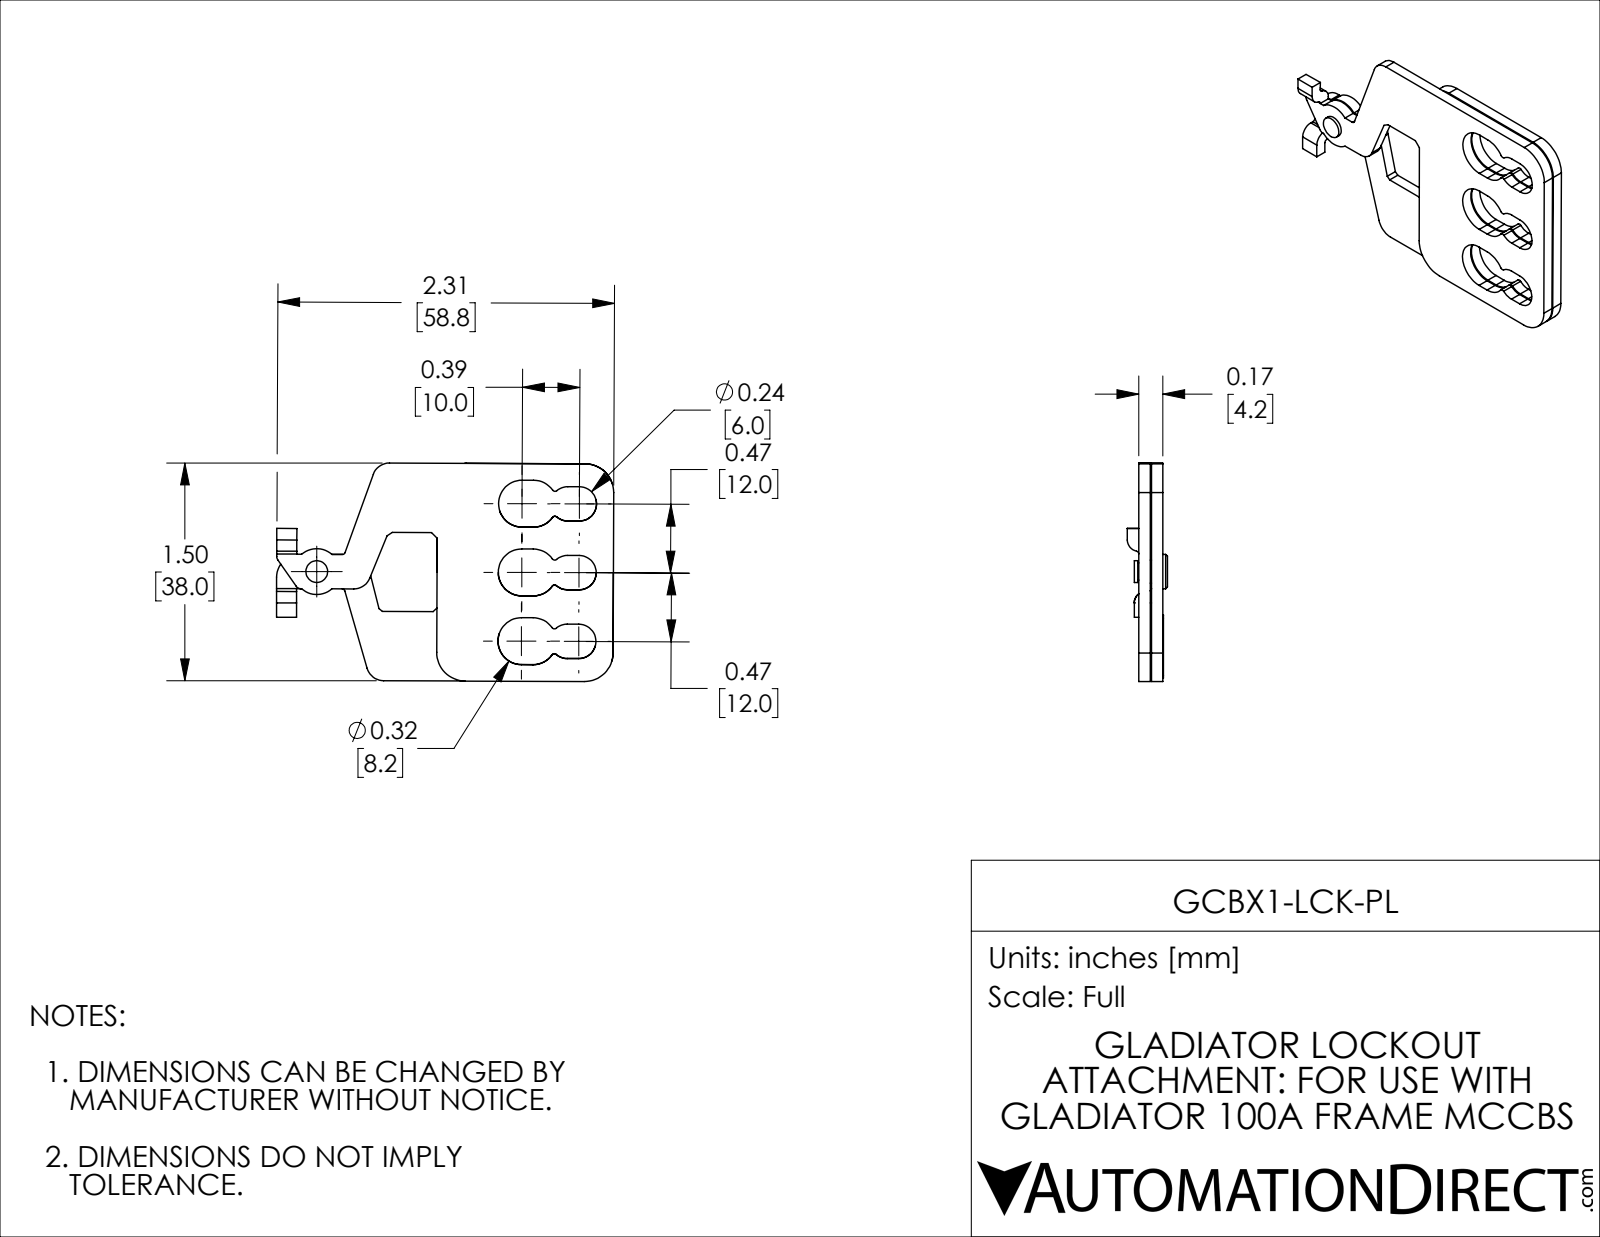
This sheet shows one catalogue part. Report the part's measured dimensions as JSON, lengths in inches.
{"part_name": "GCBX1-LCK-PL", "step_written_by": "SolidWorks 2021 (CONFIG_CONTROL_DESIGN)", "units": "inches", "bodies": {"solids": 1, "faces": 940, "planar": 822, "cylindrical": 116, "other": 2}, "overall_size": [2.319, 1.502, 0.276], "volume_in3": 0.279, "surface_area_in2": 9.308, "round_holes": [[0.126, 1], [0.165, 1]], "round_bosses_or_shafts": [[0.236, 1], [0.157, 1], [0.15, 1], [0.118, 1]], "partial_cylinders_radius": [[0.02, 22], [0.118, 16], [0.161, 12], [0.197, 6], [0.079, 4], [0.039, 2], [0.157, 2]], "face_to_face_distances": [0.079, 0.087, 0.165, 0.083, 0.091, 0.169, 1.213, 1.496, 0.118, 0.031]}
